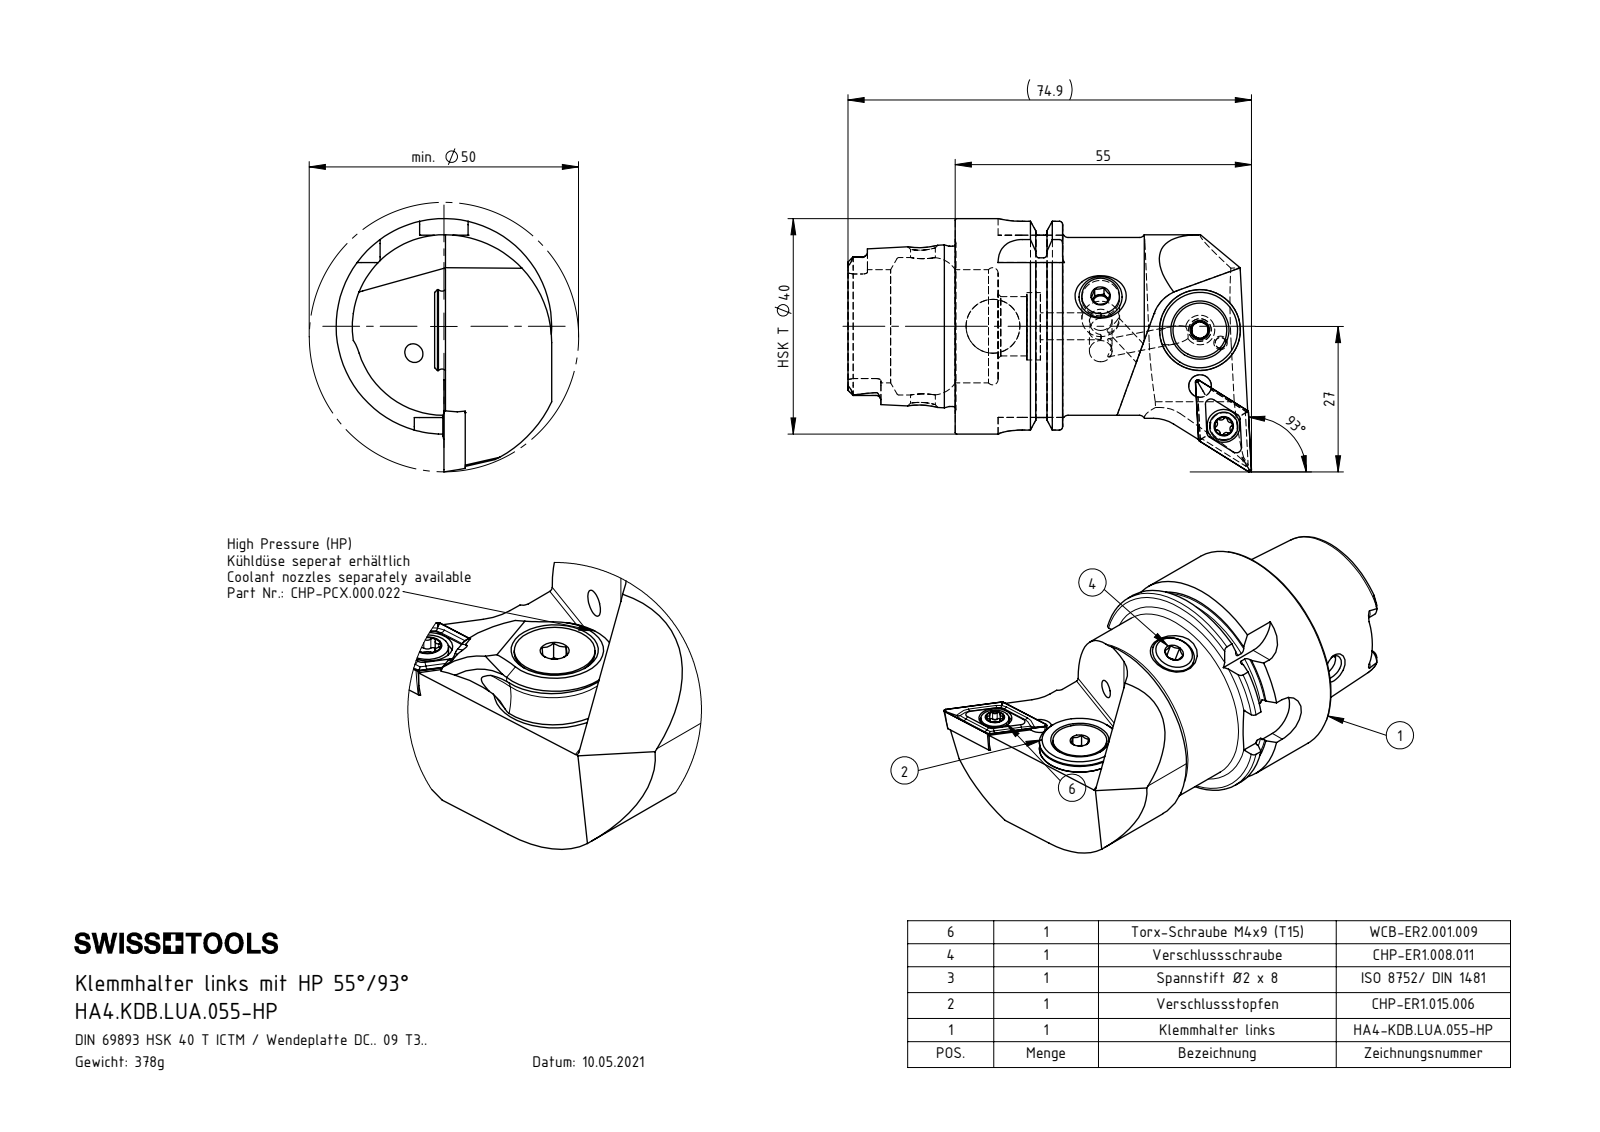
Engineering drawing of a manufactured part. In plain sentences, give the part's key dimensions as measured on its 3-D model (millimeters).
The part is named "HA4-KDB.LUA.055-HP_A_Fertigbearbeitung; CHP-ER1.015.006; DIN 7991 - M5x15; DIN 3771 - 13x1 (+6 more)". Its 3-D file was written by "SolidWorks 2022 (AUTOMOTIVE_DESIGN)". It is 8 solids with 418 faces: 116 planar, 121 cylindrical and 181 other. Overall it measures 74.9 by 47.01 by 40 millimeters. Its volume is 48 199 cubic millimeters and its surface area 16 887 square millimeters. Round holes: 3 of diameter 3.3, 3 of diameter 4.2, 1 of diameter 1.2, 1 of diameter 2, 1 of diameter 2.5, 1 of diameter 3, 1 of diameter 4.4, 1 of diameter 4.6, 1 of diameter 5, 1 of diameter 5.2, 1 of diameter 6.1, 1 of diameter 7. Round bosses or shafts: 1 of diameter 40, 1 of diameter 34.75, 1 of diameter 33, 1 of diameter 29.71, 1 of diameter 15, 1 of diameter 13.4, 1 of diameter 10, 1 of diameter 8. Partial cylindrical surfaces (rounded edges, fillets, slot ends): 6 of radius 0.34, 6 of radius 0.59, 6 of radius 0.9, 4 of radius 4.5, 2 of radius 0.4, 2 of radius 1.82, 2 of radius 1.88, 2 of radius 7. The main face-to-face distances are 4.5, 7.95, 19.95, 12, 15.2, 19.7, 16.03, 0.83, 3.67, 19.9. The hole center spacings are 4.5, 8.58, 8.67, 8.85, 10.38, 15.4, 15.48, 18.3.
